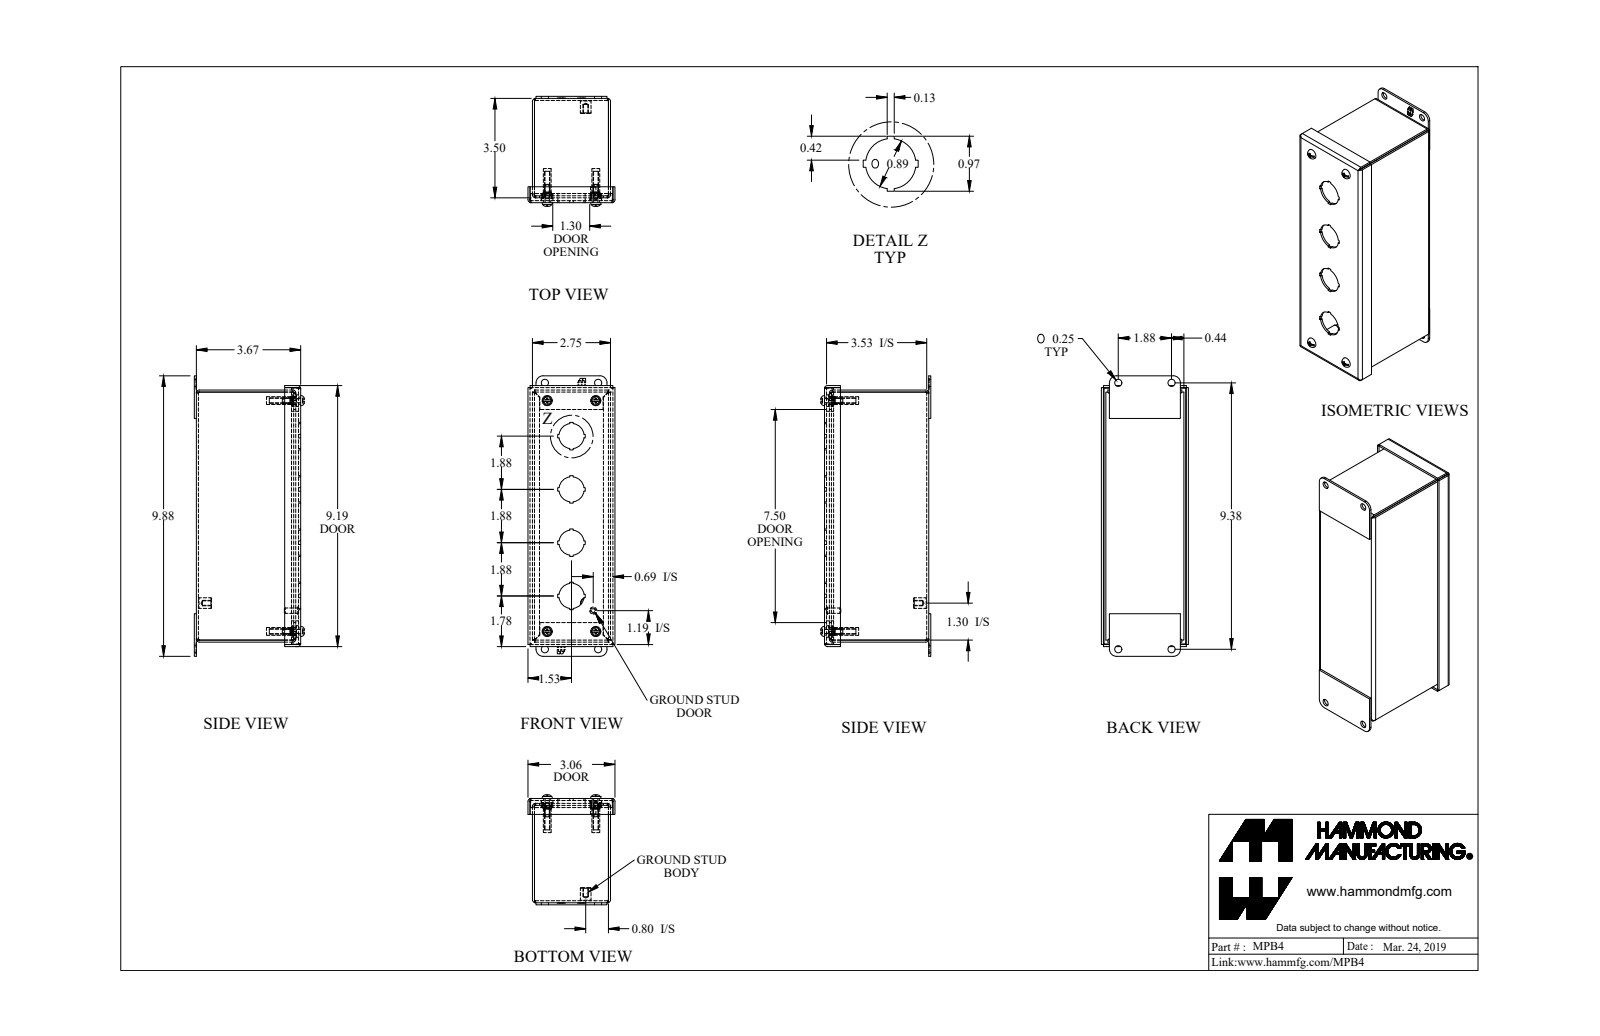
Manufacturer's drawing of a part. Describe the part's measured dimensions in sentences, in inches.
The part is named "MPB4". Its 3-D file was written by "SolidWorks 2018 (AUTOMOTIVE_DESIGN)". It is 19 solids with 619 faces: 407 planar, 156 cylindrical and 56 other. Overall it measures 9.875 by 3.871 by 3.063 inches. Its volume is 13.32 cubic inches and its surface area 349.7 square inches. Round holes: 8 of diameter 0.25, 4 of diameter 0.159, 4 of diameter 0.406, 4 of diameter 0.886, 1 of diameter 0.156. Round bosses or shafts: 4 of diameter 0.39, 4 of diameter 0.275, 4 of diameter 0.19, 4 of diameter 0.148, 1 of diameter 0.375, 1 of diameter 0.25, 1 of diameter 0.188. Partial cylindrical surfaces (rounded edges, fillets, slot ends): 12 of radius 0.036, 12 of radius 0.108, 4 of radius 0.16, 4 of radius 0.171, 4 of radius 0.25. The main face-to-face distances are 0.072, 0.072, 2.678, 3.6, 3.672, 2.75, 2.606, 3.528, 8.803, 0.156. The hole center spacings are 0.63, 1.875, 1.899, 8.75, 8.932, 1.514, 1.516, 1.709.
